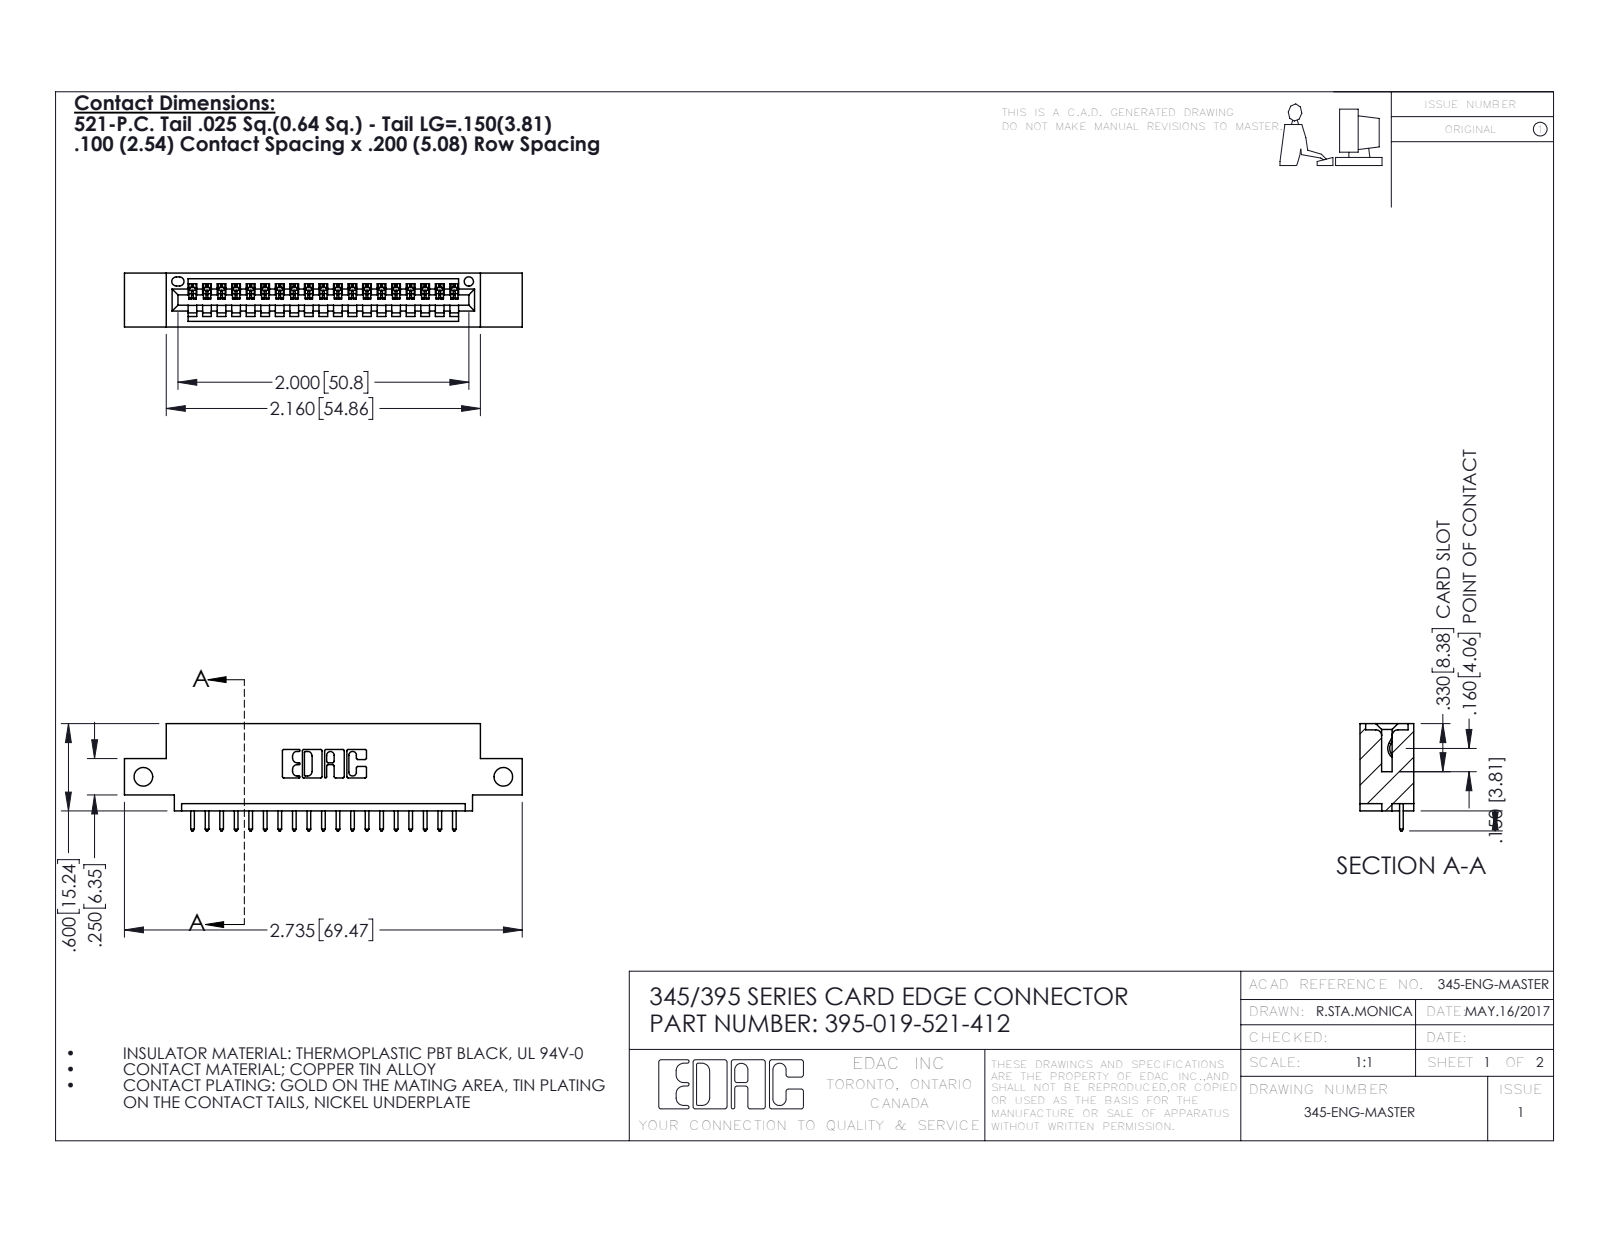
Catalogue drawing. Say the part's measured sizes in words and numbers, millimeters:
The part is named "345 Part_0.110 Offset - Side Mount; 345-292-001_345-293-121; 395-019-521-412". Its 3-D file was written by "SolidWorks 2016 (CONFIG_CONTROL_DESIGN)". It is 20 solids with 1232 faces: 844 planar, 388 cylindrical and 0 other. Overall it measures 69.5 by 18.7 by 9.4 millimeters. Its volume is 6 190 cubic millimeters and its surface area 7 652 square millimeters. Round holes: 2 of diameter 3.3, 1 of diameter 1.6. Partial cylindrical surfaces (rounded edges, fillets, slot ends): 38 of radius 0.2, 38 of radius 0.3, 22 of radius 0.3, 6 of radius 0.2, 6 of radius 0.8, 3 of radius 0.7, 2 of radius 0.8, 2 of radius 1. The main face-to-face distances are 1.8, 7.6, 9.4, 5.1, 2.5, 6.9, 0.6, 5.7, 3.8, 15.2. The hole center spacings are 62.9.
